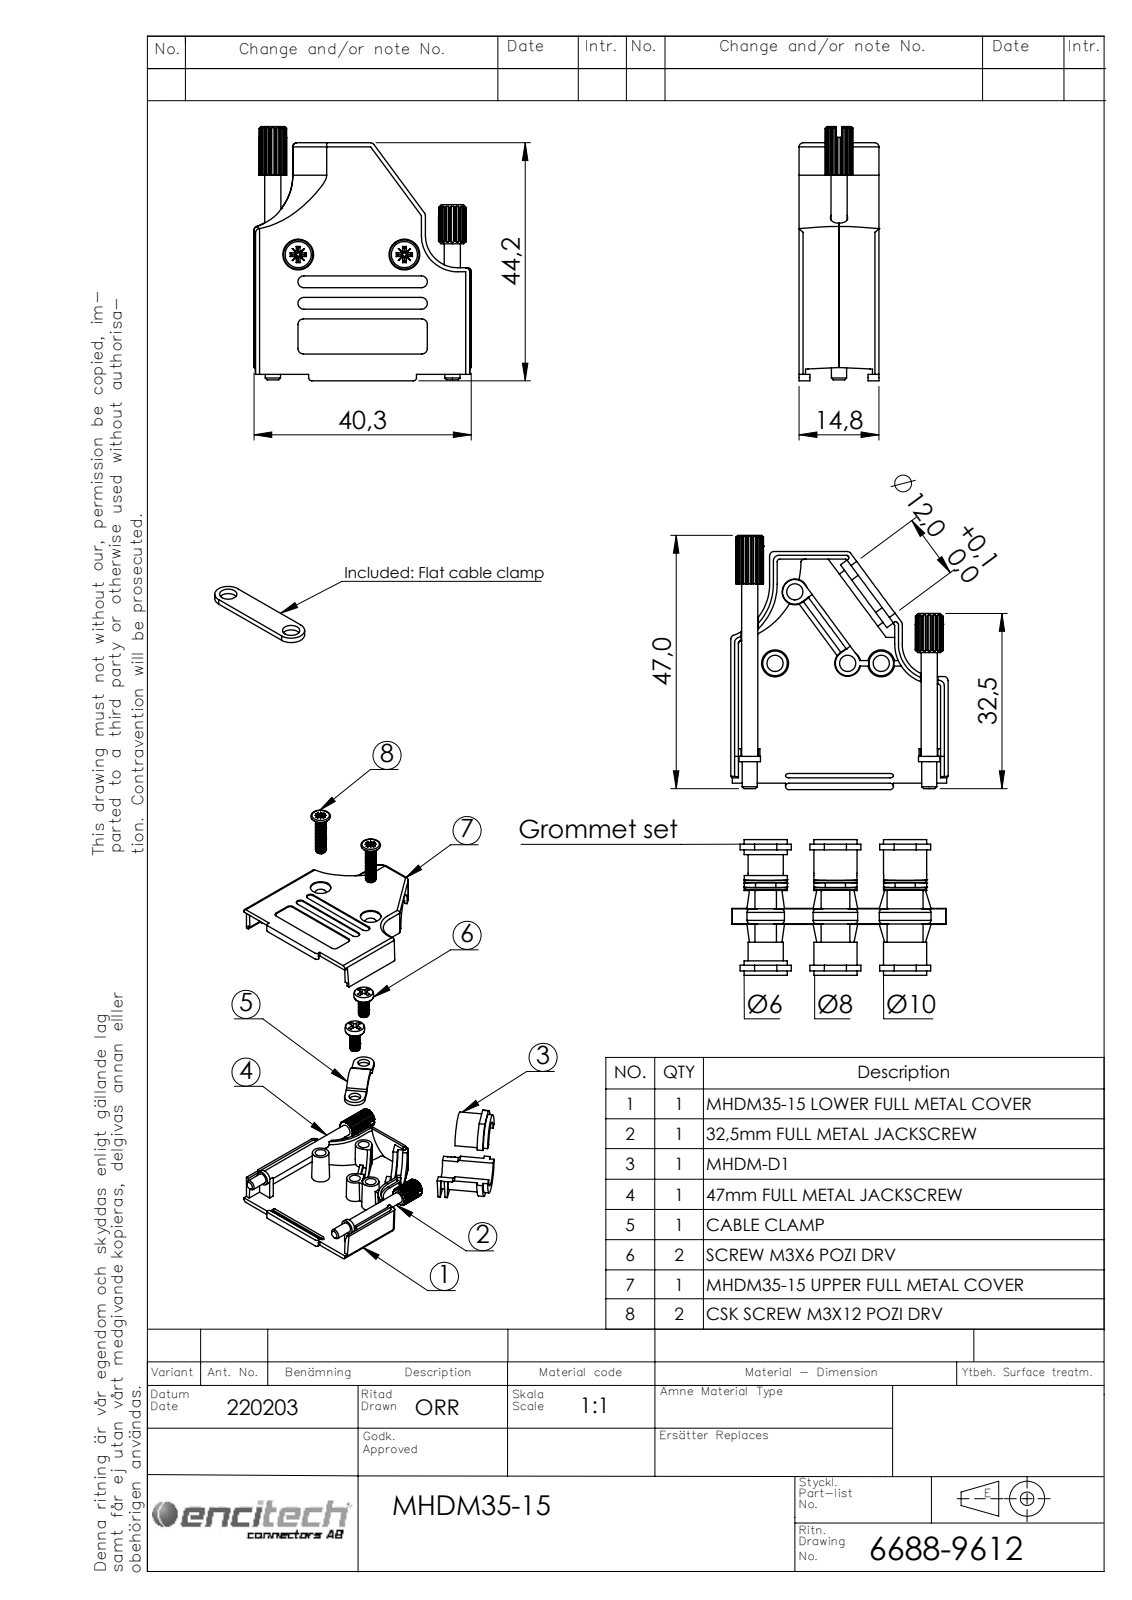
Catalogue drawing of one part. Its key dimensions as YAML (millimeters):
part_name: "6522-0122-03 (8mm LV); 6805-0139-02; 6826-0141-01; 6560-0139-12 (+6 more)"
step_written_by: "SolidWorks 2021 (AUTOMOTIVE_DESIGN)"
units: millimeters
bodies: {solids: 11, faces: 856, planar: 415, cylindrical: 318, other: 123}
overall_size: [47.2, 40.3, 14.8]
volume: 7465
surface_area: 13007
round_holes:
  - {diameter: 3, count: 4}
  - {diameter: 3.2, count: 4}
  - {diameter: 4.8, count: 2}
  - {diameter: 5.7, count: 2}
  - {diameter: 8, count: 1}
  - {diameter: 12, count: 1}
round_bosses_or_shafts:
  - {diameter: 2.9, count: 4}
  - {diameter: 4, count: 2}
  - {diameter: 3, count: 2}
  - {diameter: 2.8, count: 2}
  - {diameter: 12, count: 1}
partial_cylinders:
  - {radius: 0.75, count: 16}
  - {radius: 1, count: 9}
  - {radius: 0.1, count: 8}
  - {radius: 0.3, count: 5}
  - {radius: 0.5, count: 5}
  - {radius: 1.1, count: 4}
  - {radius: 0.38, count: 3}
  - {radius: 0.6, count: 2}
face_to_face_distances: [1.2, 13.6, 12.4, 14.8, 6.2, 7.4, 7.1, 0.9, 13.3, 14.5]
hole_center_spacings: [6.23, 13.47, 13.77, 16.5, 19.7, 20.81, 33.3]
